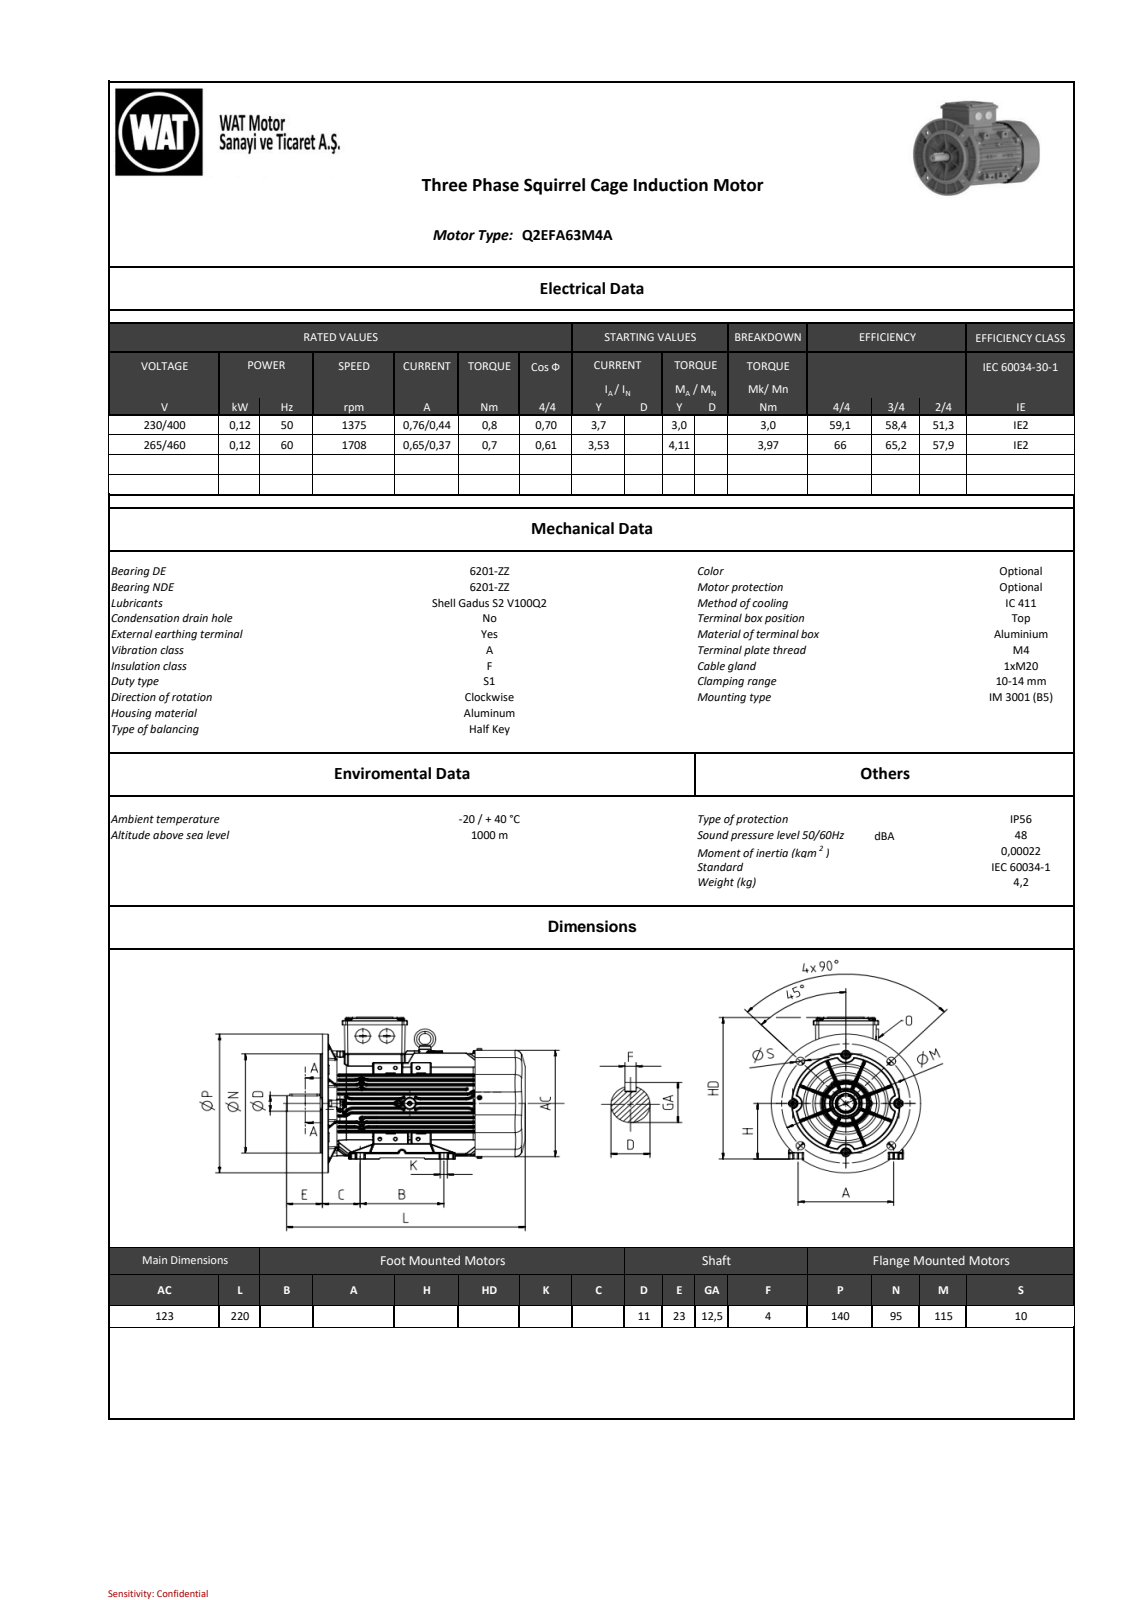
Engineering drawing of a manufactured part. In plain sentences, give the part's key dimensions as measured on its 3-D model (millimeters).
The part is named "QS63FAGMM_new". Its 3-D file was written by "UNIX (AUTOMOTIVE_DESIGN)". It is 9 solids with 2630 faces: 0 planar, 0 cylindrical and 2630 other. Overall it measures 219.46 by 167.2 by 140.2 millimeters. Its volume is 32 494 cubic millimeters and its surface area 371 297 square millimeters.
